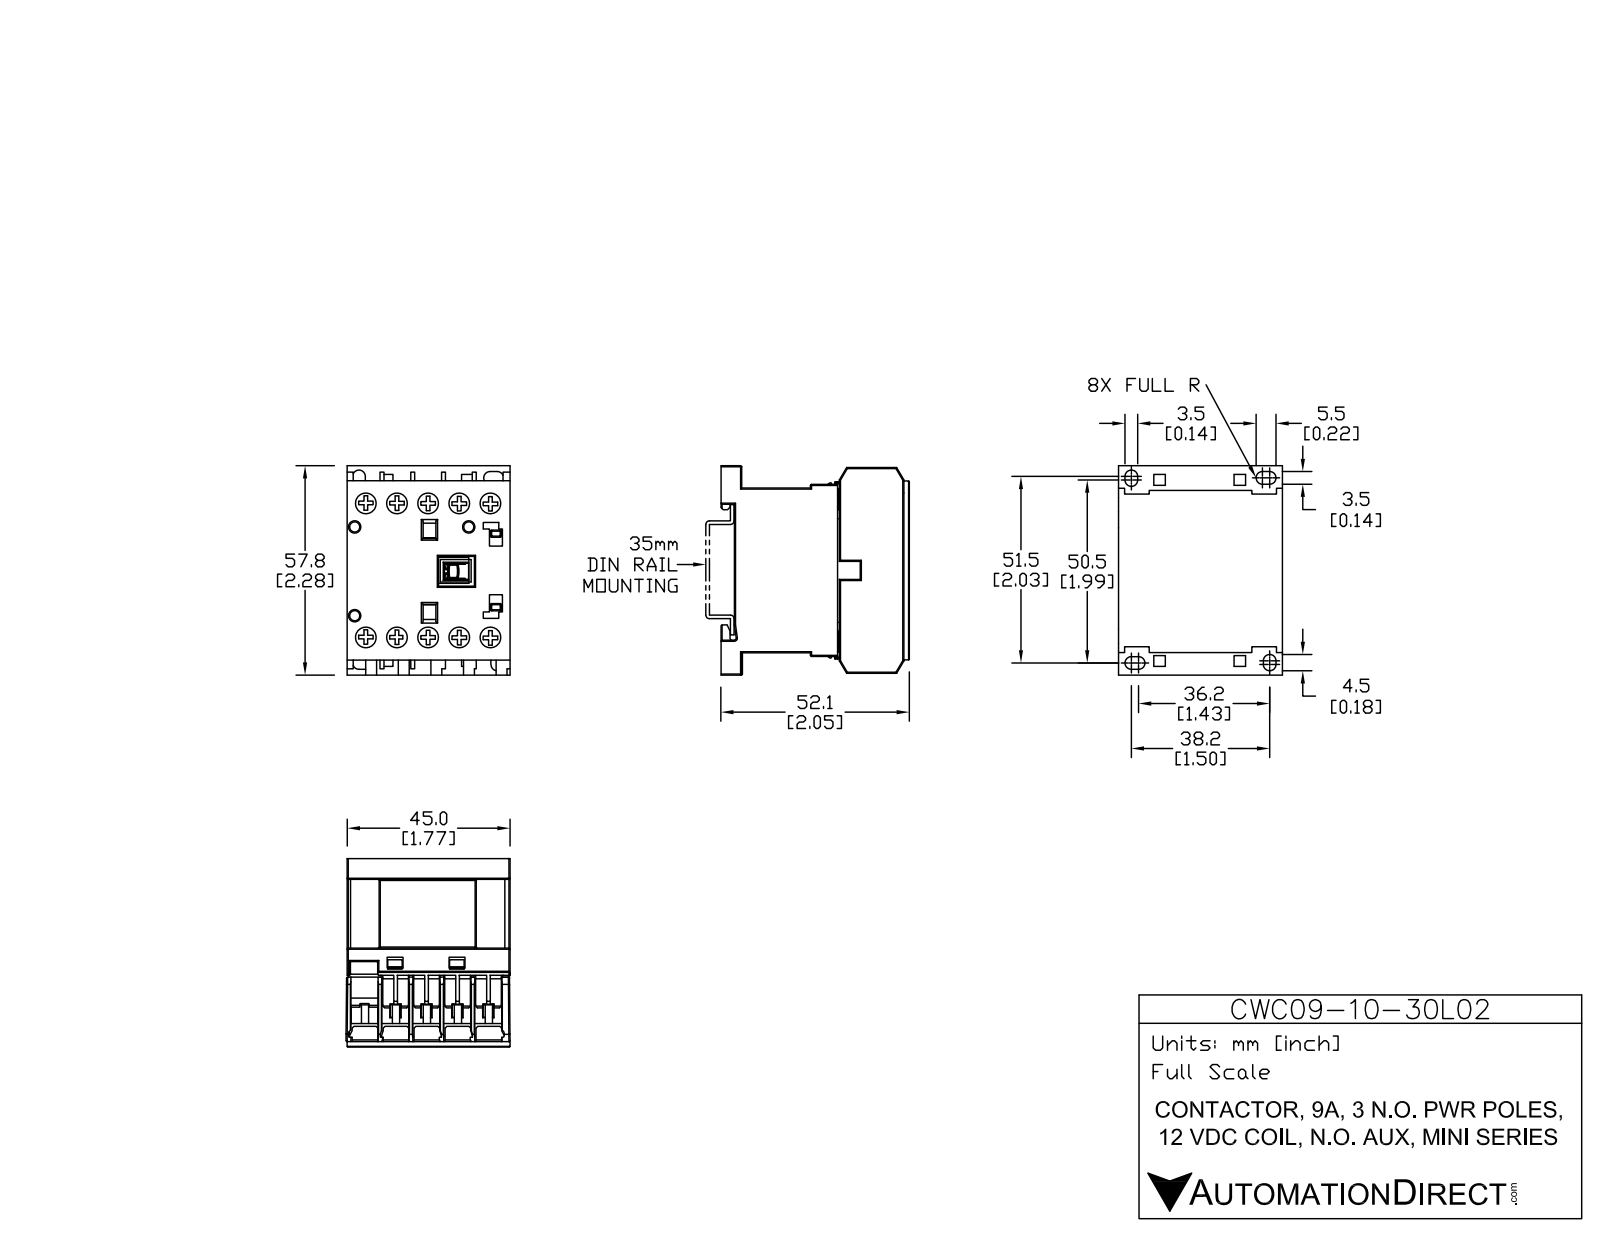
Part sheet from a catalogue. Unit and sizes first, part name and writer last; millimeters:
Units: millimetres
Overall size (bounding box): 58.04 × 52.12 × 45.75
Round holes (diameter × count): ⌀6.2 ×10, ⌀2.8 ×3
Round bosses / shafts (diameter × count): ⌀5.9 ×10
Partial cylindrical surfaces — rounded edges, fillets, slot ends (radius × count): R0.3 ×20, R1.72 ×6, R1.73 ×2, R0.32 ×1, R0.42 ×1, R0.55 ×1
Main face-to-face distances: 8.25, 45.5, 1.25, 16.5, 9.5, 5.5, 17.75, 5.13, 10.63, 7
Hole centre spacings: 8.55, 37.94, 17.1, 40.72, 36.96, 25.65, 44.99, 6.91
Volume: 97 133 mm³ · Surface area: 30 437 mm²
Bodies: 15 solids, 535 faces (445 planar, 90 cylindrical, 0 other)
Part name (STEP PRODUCT): CWC09-10-30L02
STEP written by: SolidWorks 2013 (AUTOMOTIVE_DESIGN)
